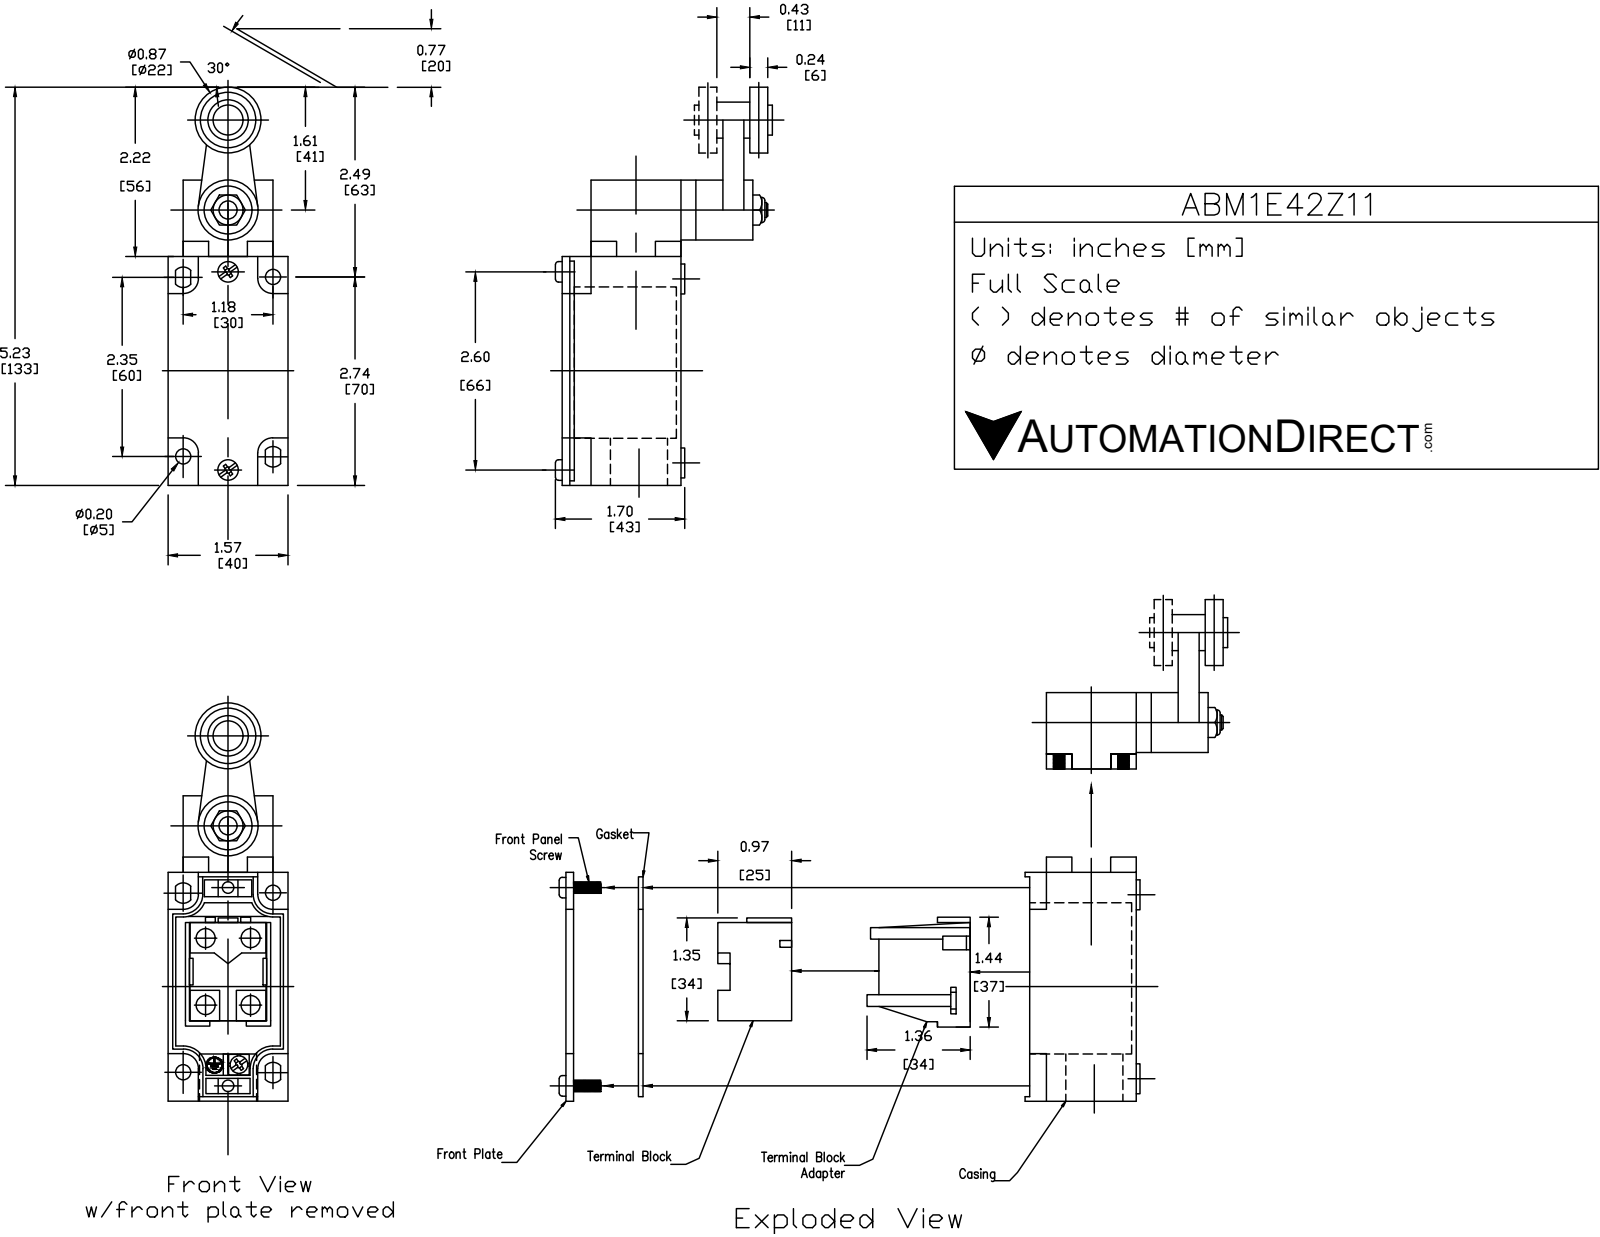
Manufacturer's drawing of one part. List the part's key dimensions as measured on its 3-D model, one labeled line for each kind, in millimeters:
Part name (STEP PRODUCT): ABM1E42Z11
STEP written by: SolidWorks 2017 (AUTOMOTIVE_DESIGN)
Units: millimetres
Bodies: 3 solids, 223 faces (90 planar, 92 cylindrical, 41 other)
Overall size (bounding box): 133 × 61 × 40
Volume: 143 900 mm³ · Surface area: 28 620 mm²
Round holes (diameter × count): ⌀5.2 ×2, ⌀14 ×1, ⌀17 ×1, ⌀19 ×1
Round bosses / shafts (diameter × count): ⌀10 ×6, ⌀7 ×3, ⌀22 ×1, ⌀20 ×1, ⌀11.5 ×1, ⌀6 ×1
Partial cylindrical surfaces — rounded edges, fillets, slot ends (radius × count): R1.5 ×16, R1 ×4, R5 ×4, R3.3 ×2, R6 ×1, R11.5 ×1, R12 ×1
Main face-to-face distances: 40, 39.5, 5, 30, 35, 76.5, 25, 9.5, 0.5, 102
Hole centre spacings: 26.6, 67.1, 83.4
